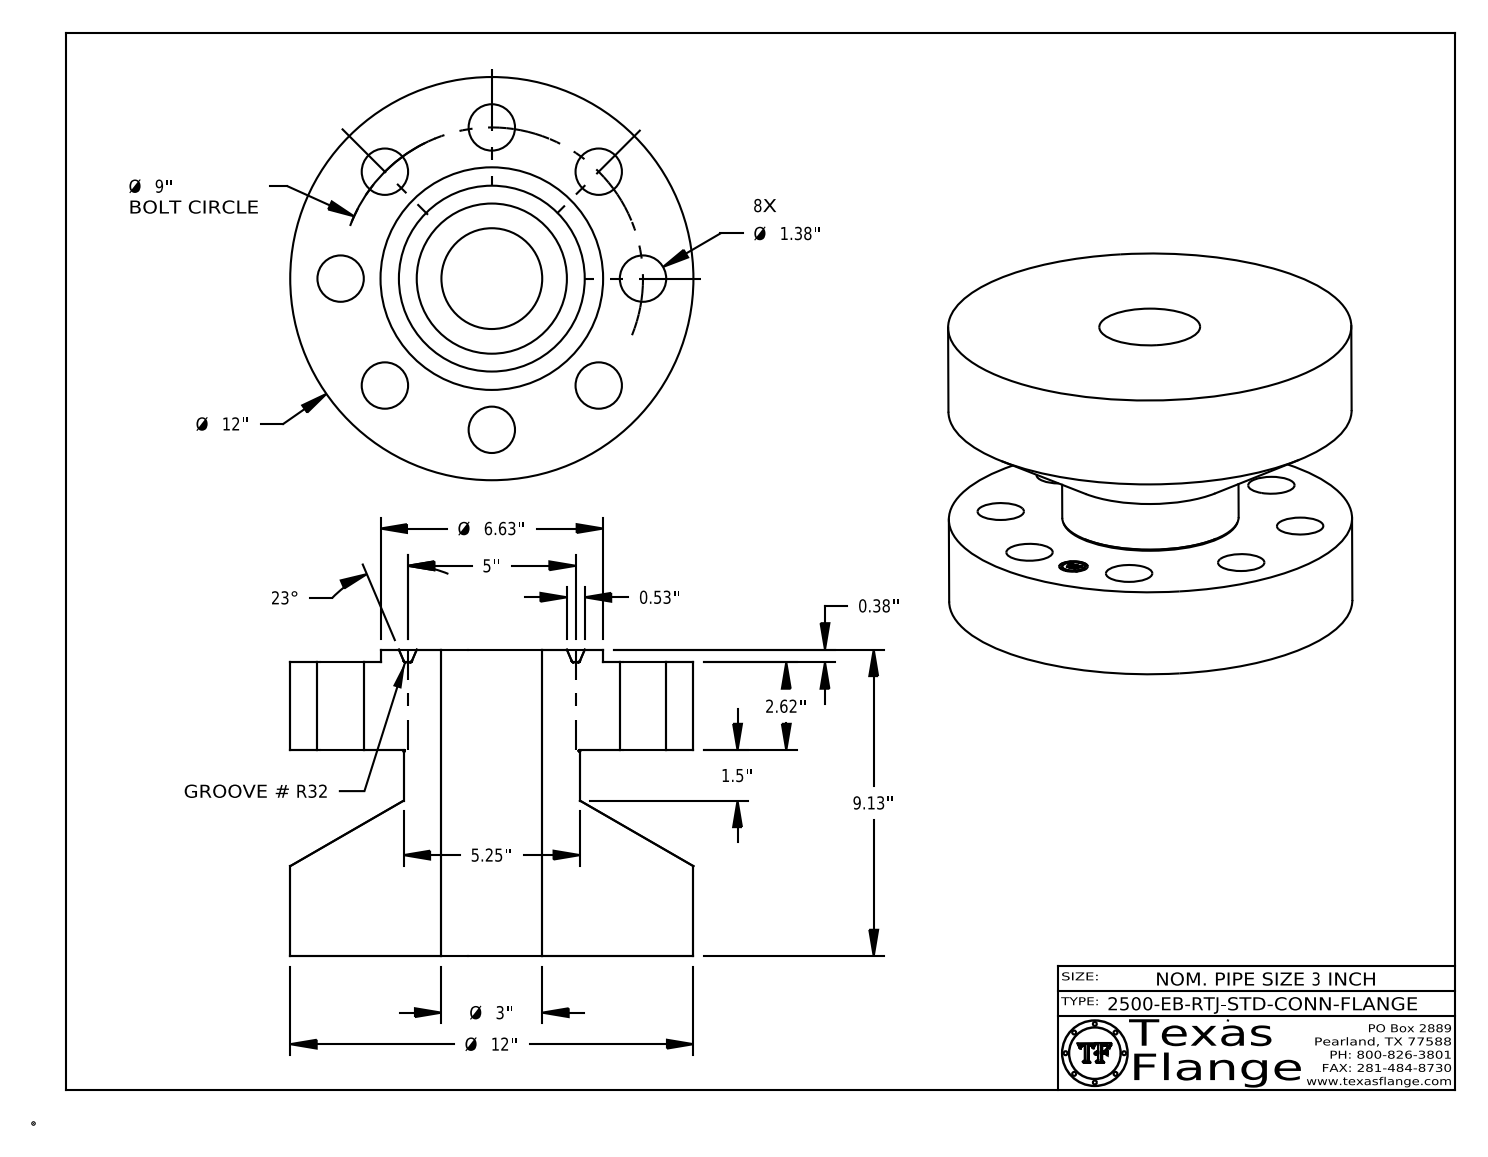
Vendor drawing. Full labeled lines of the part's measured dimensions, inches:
Part name (STEP PRODUCT): 3-2500-EB-RTJ-STD-CONN-FLANGE
STEP written by: CATIA V5 STEP AP214 (AUTOMOTIVE_DESIGN)
Units: inches
Bodies: 1 solid, 431 faces (371 planar, 46 cylindrical, 14 other)
Overall size (bounding box): 12 × 12 × 9.125
Volume: 666.6 in³ · Surface area: 802.6 in²
Round holes (diameter × count): ⌀1.38 ×8, ⌀0.85 ×1, ⌀3 ×1
Round bosses / shafts (diameter × count): ⌀0.051 ×8, ⌀12 ×1, ⌀6.625 ×1, ⌀5.25 ×1, ⌀0.67 ×1
Main face-to-face distances: 6.13, 2.62, 8.75, 0.375, 2.995, 9.125, 2.99, 2.615, 6.135, 0.254
Hole centre spacings: 4.5, 3.444, 6.364, 8.315, 1.756, 5, 7.483, 9
